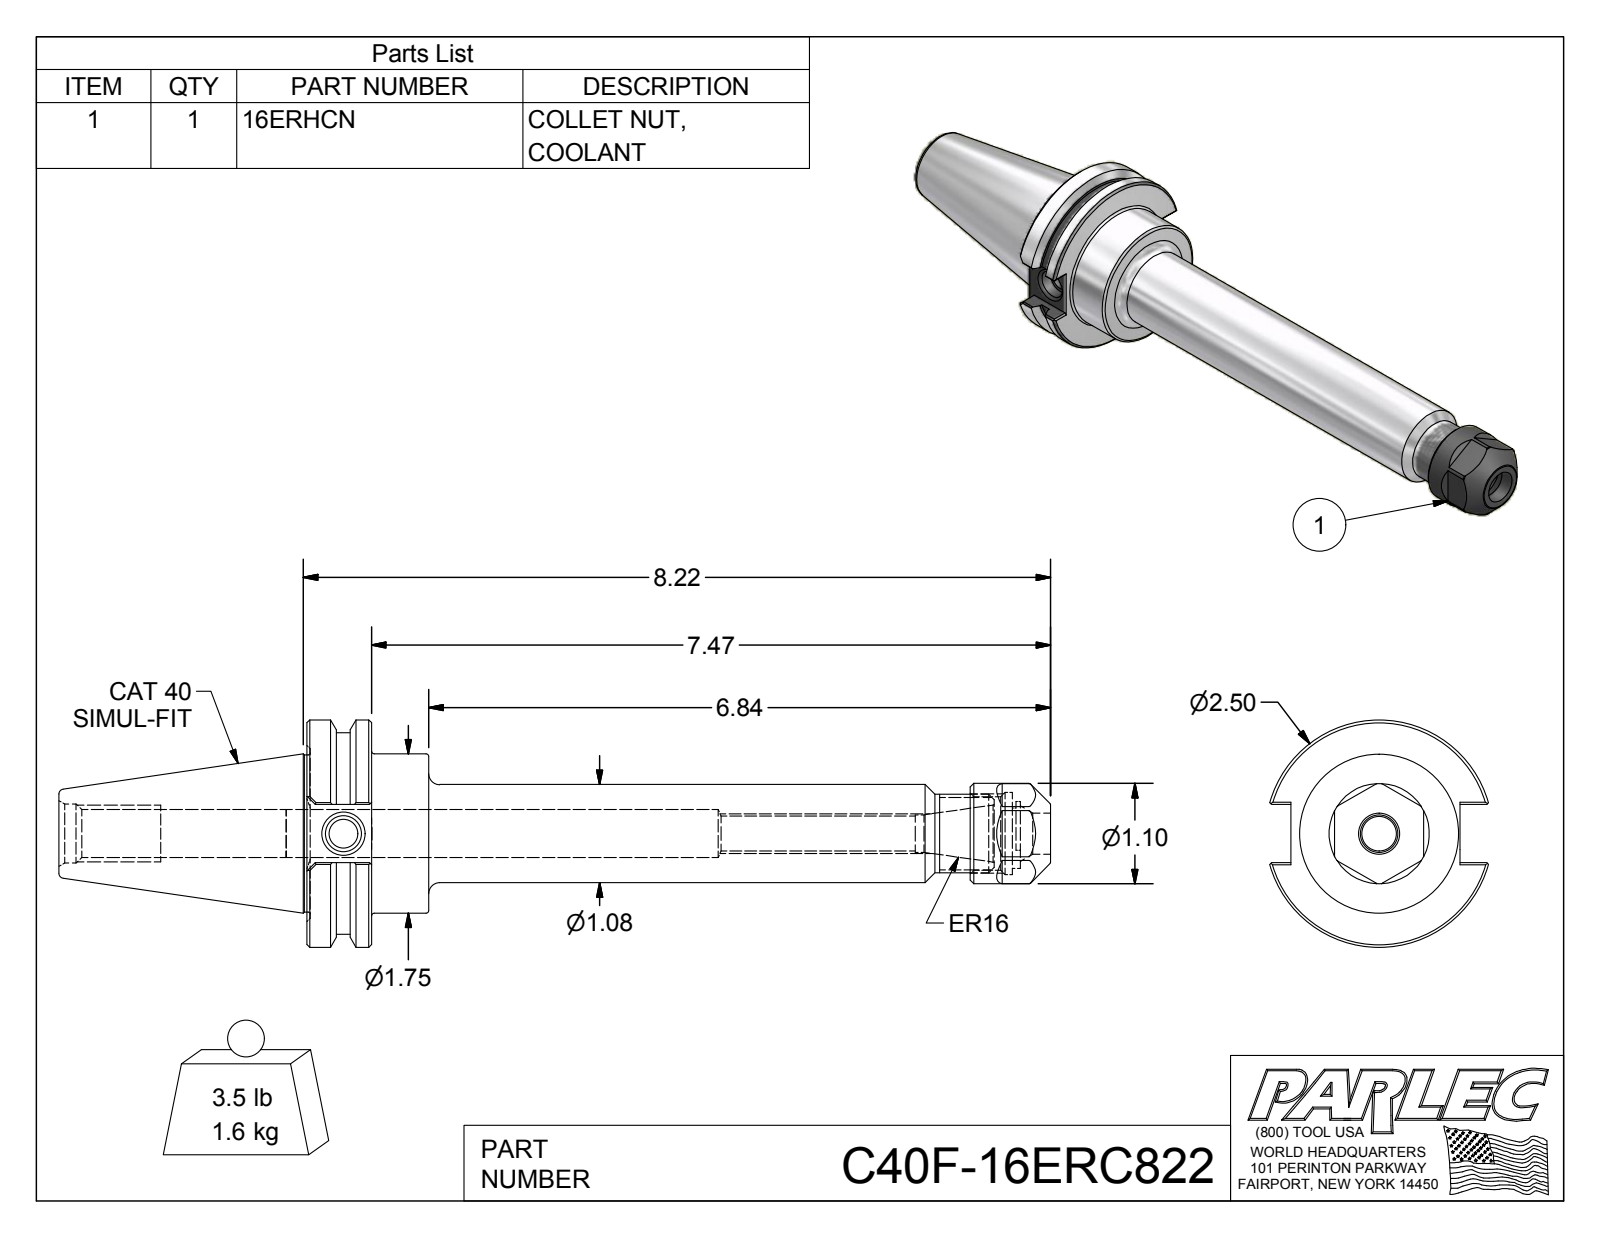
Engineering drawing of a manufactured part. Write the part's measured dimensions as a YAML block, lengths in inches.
part_name: "C40F-16ERC822; C40F-16ER8-1; 16ERHCN"
step_written_by: "Autodesk Inventor 2012 (AUTOMOTIVE_DESIGN)"
units: inches
bodies: {solids: 2, faces: 116, planar: 51, cylindrical: 23, other: 42}
overall_size: [10.908, 2.5, 2.406]
volume: 12.38
surface_area: 71.74
round_holes:
  - {diameter: 0.315, count: 1}
  - {diameter: 0.383, count: 1}
  - {diameter: 0.399, count: 1}
  - {diameter: 0.413, count: 1}
  - {diameter: 0.453, count: 1}
  - {diameter: 0.527, count: 1}
  - {diameter: 0.527, count: 1}
  - {diameter: 0.648, count: 1}
  - {diameter: 0.661, count: 1}
  - {diameter: 0.807, count: 1}
  - {diameter: 0.906, count: 1}
round_bosses_or_shafts:
  - {diameter: 2.5, count: 1}
  - {diameter: 2.215, count: 1}
  - {diameter: 1.75, count: 1}
  - {diameter: 1.73, count: 1}
  - {diameter: 1.102, count: 1}
  - {diameter: 1.08, count: 1}
  - {diameter: 0.866, count: 1}
partial_cylinders:
  - {radius: 0.354, count: 1}
face_to_face_distances: [0.711, 1.341, 0.63, 0.979, 7.759, 7.049, 6.419, 1.86, 0.64, 0.037]
hole_center_spacings: [0.051]
